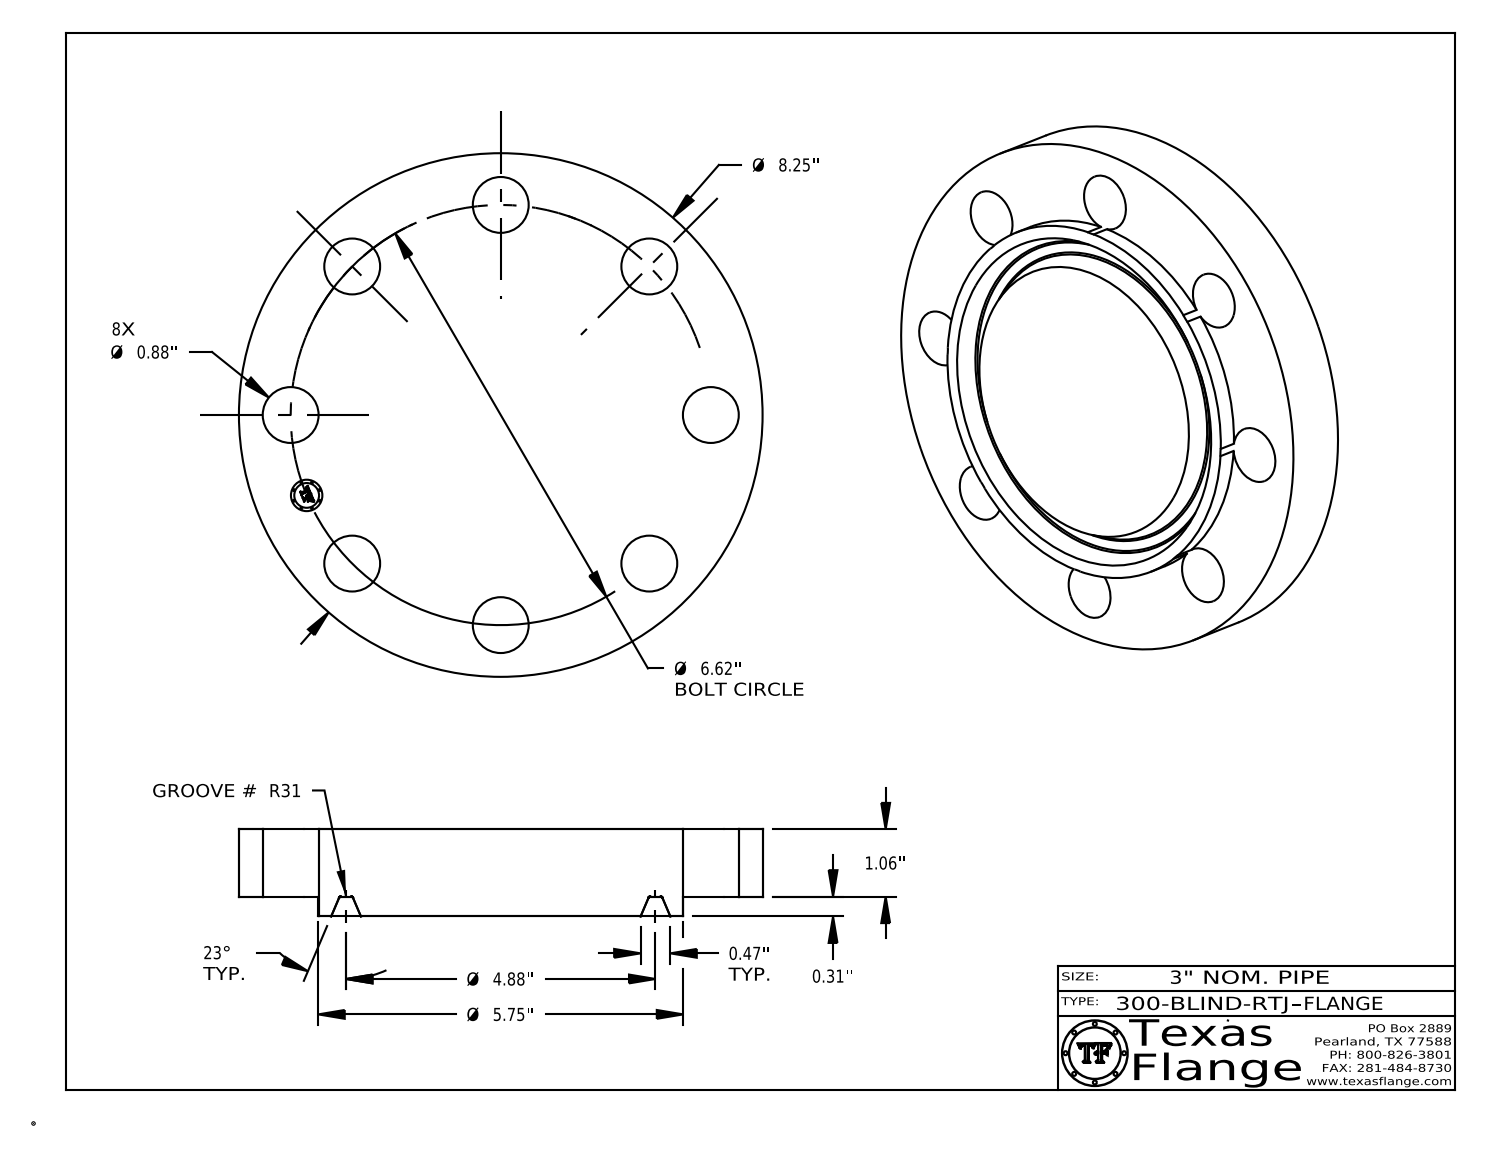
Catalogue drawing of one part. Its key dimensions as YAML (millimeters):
part_name: "300-BLIND-RTJ"
step_written_by: "CATIA V5 STEP AP214 (AUTOMOTIVE_DESIGN)"
units: millimeters
bodies: {solids: 1, faces: 426, planar: 370, cylindrical: 48, other: 8}
overall_size: [209.6, 209.6, 34.9]
volume: 950600
surface_area: 103200
round_holes:
  - {diameter: 22.4, count: 8}
  - {diameter: 12.6, count: 1}
round_bosses_or_shafts:
  - {diameter: 0.8, count: 8}
  - {diameter: 209.6, count: 1}
  - {diameter: 146.1, count: 1}
  - {diameter: 9.9, count: 1}
face_to_face_distances: [26.9, 8, 34.8, 0.4, 34.5, 26.5, 3.8, 3.7, 0.7, 2.4]
hole_center_spacings: [64.3, 155.3, 118.9, 118.9, 32.8, 93.4, 164.9, 168.1]
